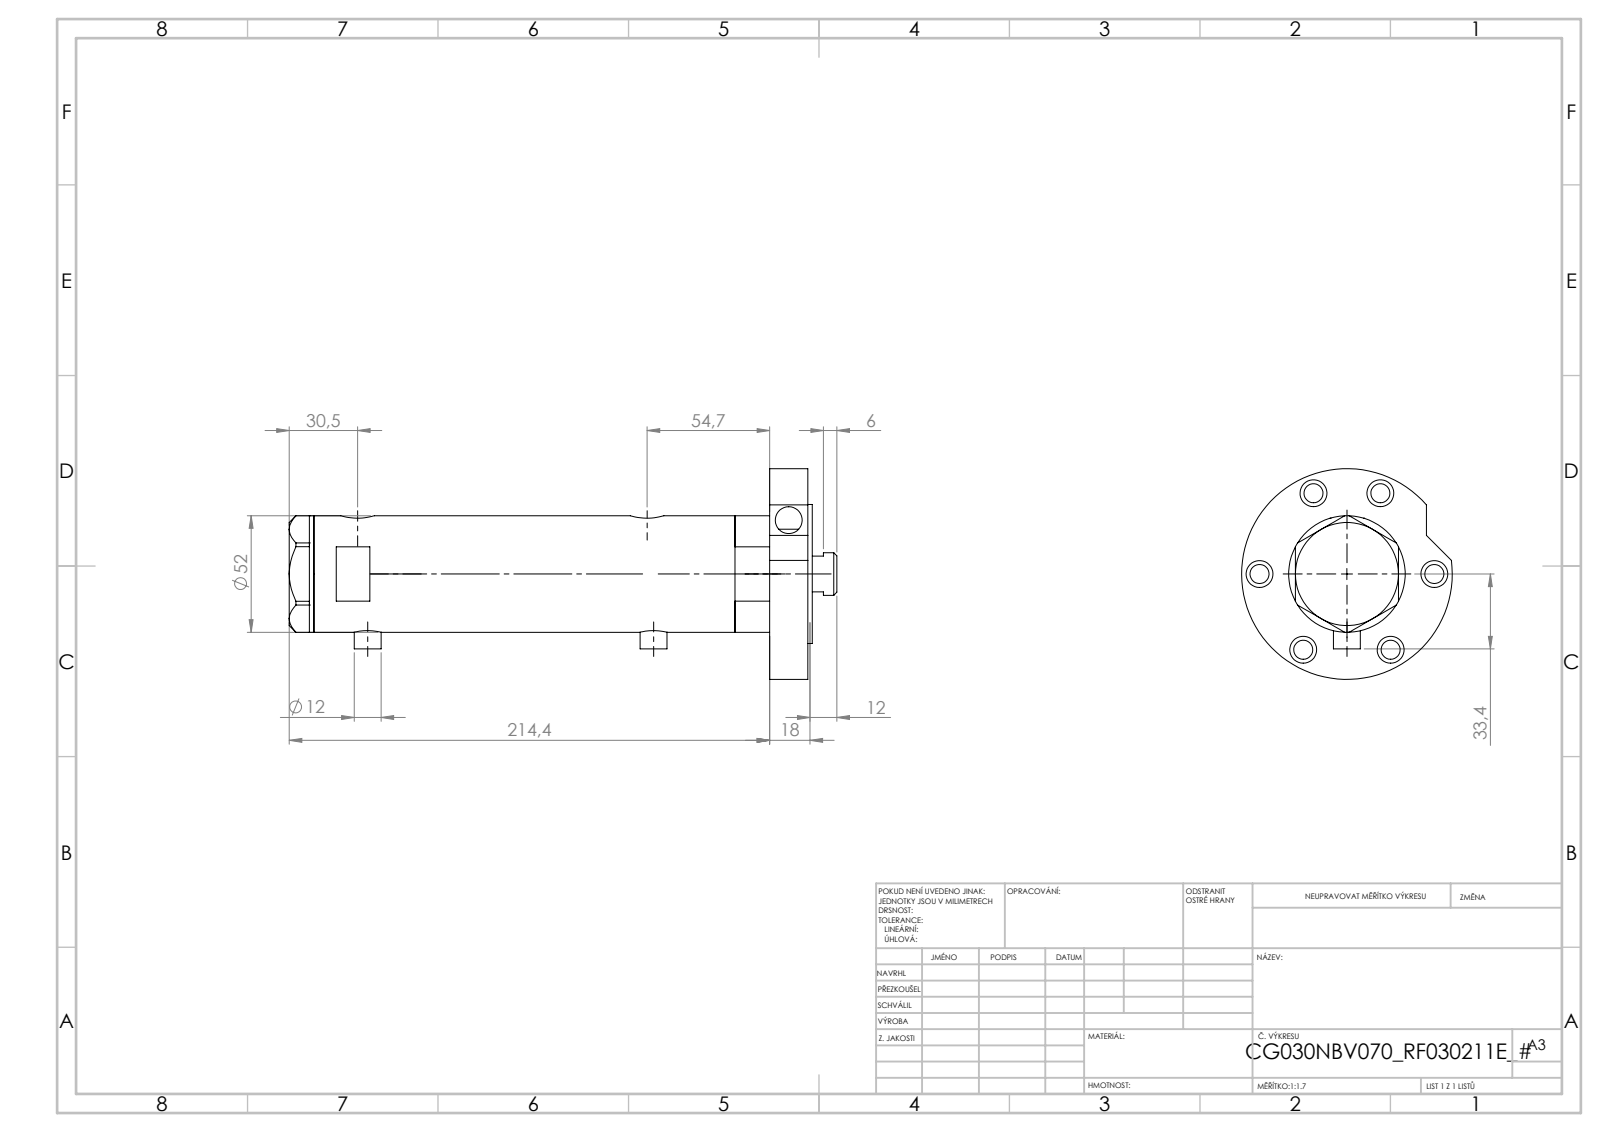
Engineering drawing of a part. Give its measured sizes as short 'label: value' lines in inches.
name: V270CG_MIDDLE; V270CG_VC; V270CG_FRONT; V270CG_RF211E (+1 more)
written by: SolidWorks 2019 (CONFIG_CONTROL_DESIGN)
unit: in
bodies: 5 solids, 178 faces (76 planar, 82 cylindrical, 20 other)
size: 9.622 × 3.701 × 3.701
volume: 32.25 in³; area: 187.2 in²
holes: 7× ⌀0.472, 6× ⌀0.335, 2× ⌀0.383, 2× ⌀0.492, 2× ⌀0.591, 1× ⌀0.256, 1× ⌀0.787, 1× ⌀0.846, 1× ⌀1.181, 1× ⌀1.299, 1× ⌀1.575, 1× ⌀1.732
bosses: 2× ⌀0.472, 1× ⌀3.701, 1× ⌀2.441, 1× ⌀2.047, 1× ⌀1.496, 1× ⌀0.748
face distances: 0.669, 8.008, 8.677, 0.079, 8.756, 5.965, 2.043, 2.713, 0.433, 9.189
hole spacings: 1.535, 1.706, 2.553, 2.659, 2.754, 3.064, 0.114, 0.177
